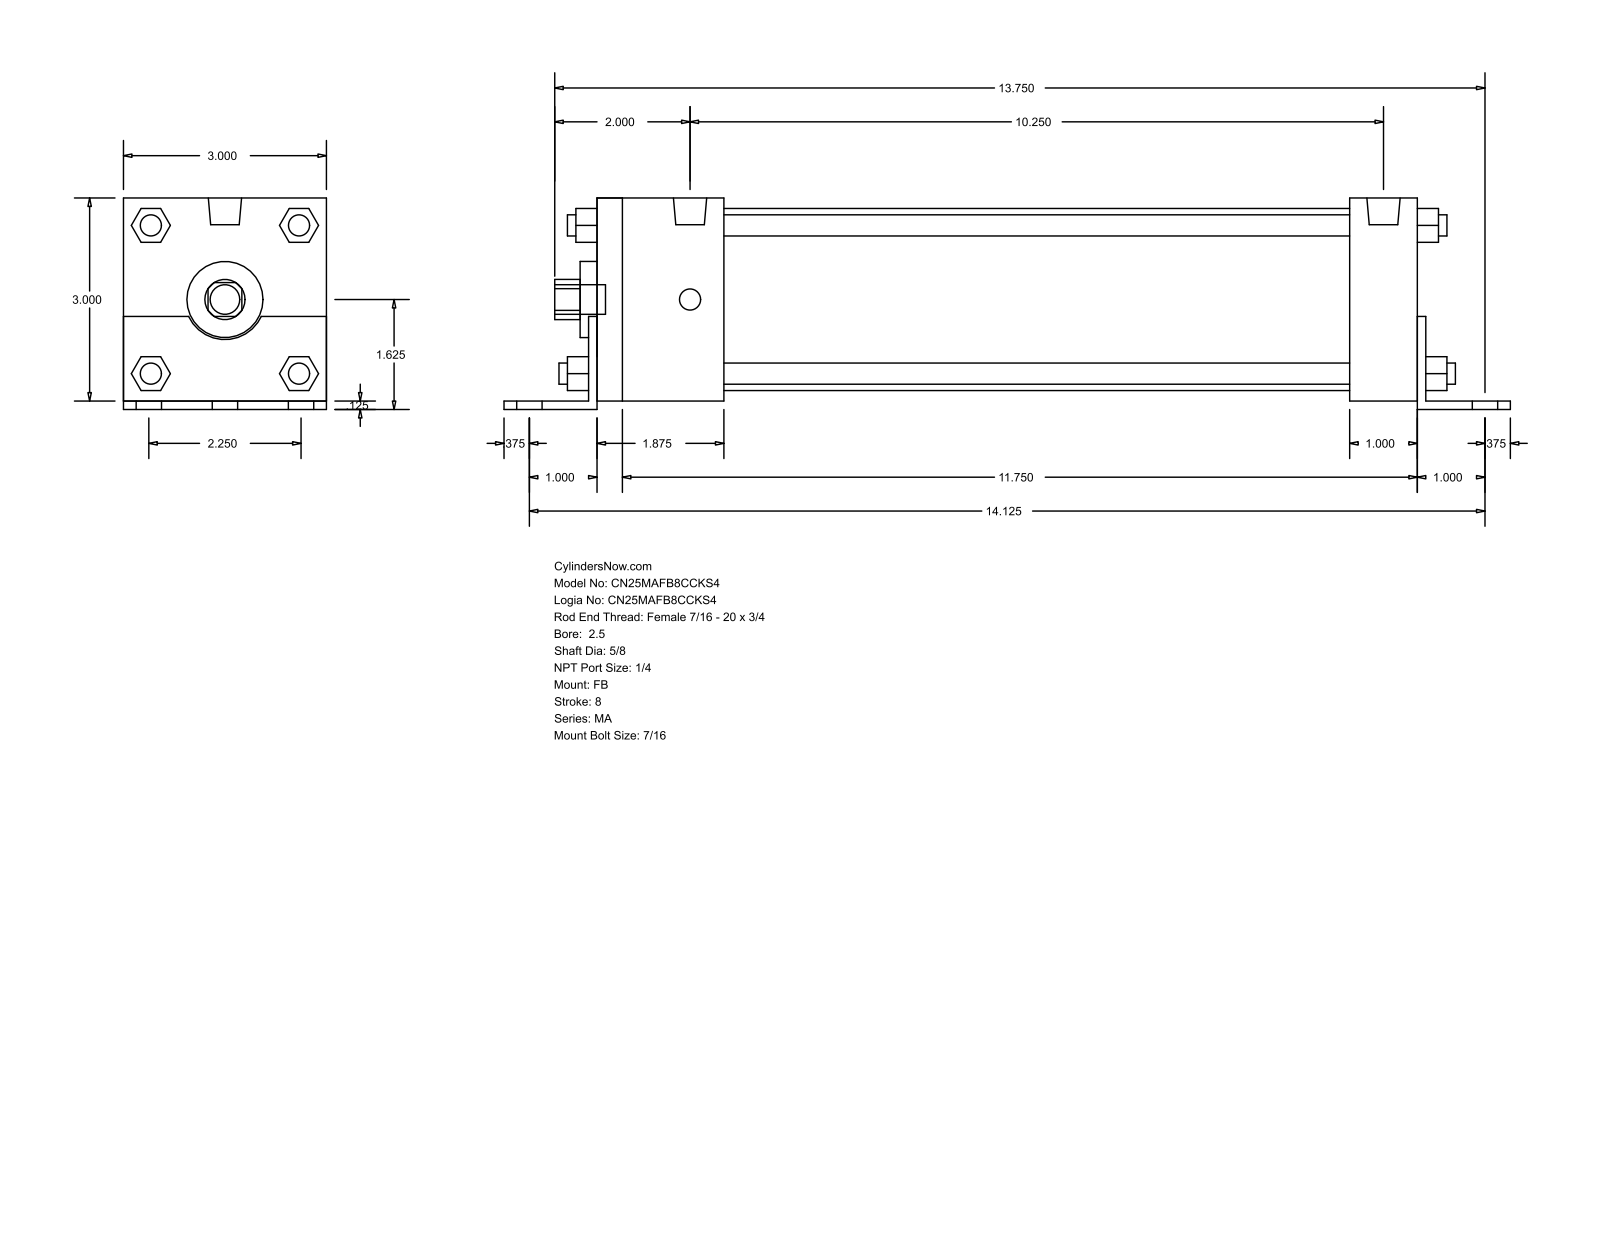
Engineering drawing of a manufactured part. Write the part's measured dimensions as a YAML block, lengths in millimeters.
part_name: "MA_FB__0250_0.625"
step_written_by: "GSSL Pune (CONFIG_CONTROL_DESIGN)"
units: millimeters
bodies: {solids: 0, faces: 140, planar: 105, cylindrical: 35, other: 0}
overall_size: [377.82, 79.38, 76.2]
round_holes:
  - {diameter: 15.88, count: 1}
  - {diameter: 28.57, count: 1}
  - {diameter: 68.33, count: 1}
round_bosses_or_shafts:
  - {diameter: 7.94, count: 8}
  - {diameter: 11.11, count: 7}
  - {diameter: 12.49, count: 2}
partial_cylinders:
  - {radius: 7.54, count: 1}
  - {radius: 15.05, count: 1}
face_to_face_distances: [76.2, 3.17, 79.37, 307.97, 314.32, 3.18, 311.14, 47.62, 25.4, 311.15]
